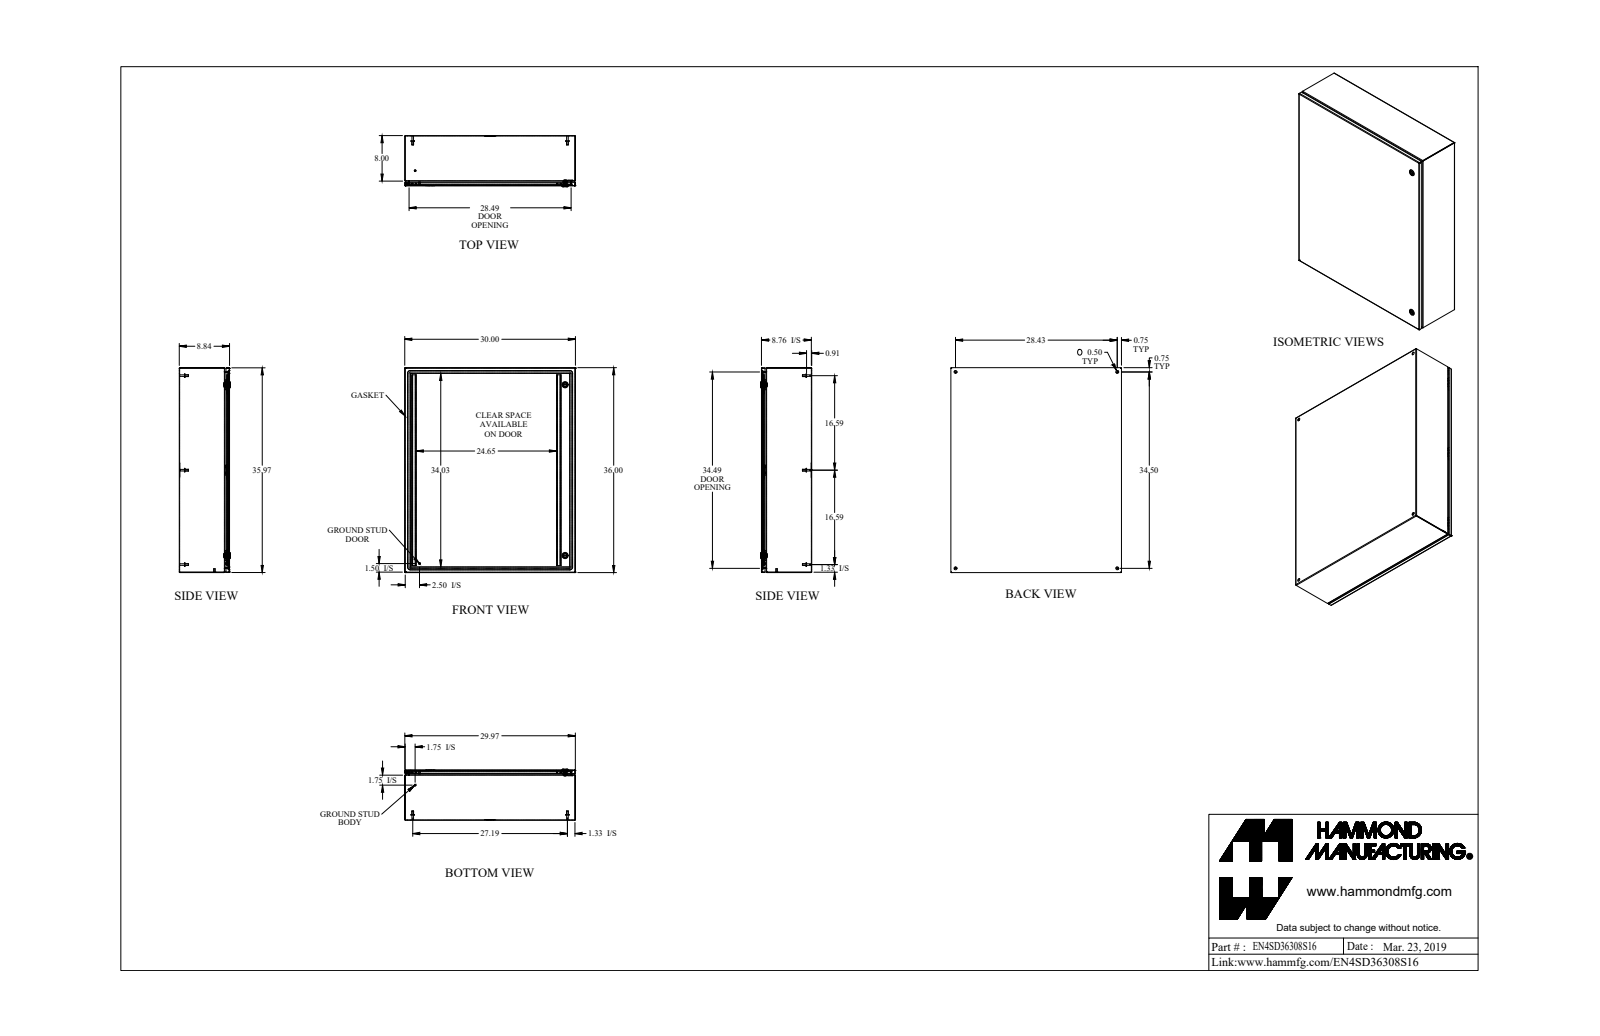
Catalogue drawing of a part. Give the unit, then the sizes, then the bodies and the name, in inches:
Units: inches
Overall size (bounding box): 36 × 30 × 9.002
Round holes (diameter × count): ⌀0.5 ×6, ⌀0.197 ×2, ⌀0.387 ×2, ⌀0.63 ×2, ⌀0.768 ×2, ⌀0.172 ×1, ⌀0.24 ×1, ⌀0.242 ×1
Round bosses / shafts (diameter × count): ⌀0.625 ×8, ⌀0.313 ×8, ⌀0.275 ×6, ⌀1.1 ×2, ⌀0.785 ×2, ⌀0.525 ×2, ⌀0.25 ×2, ⌀0.236 ×2
Partial cylindrical surfaces — rounded edges, fillets, slot ends (radius × count): R0.036 ×20, R0.108 ×20, R0.25 ×16, R0.01 ×12, R0.048 ×12, R0.006 ×6, R0.062 ×6, R0.125 ×4
Main face-to-face distances: 0.072, 8.77, 8.698, 8.842, 29.928, 35.928, 29.856, 30, 35.856, 36
Hole centre spacings: 27.531, 28.428, 34.5, 44.704, 2.457, 2.458, 30, 32.265
Volume: 267.6 in³ · Surface area: 7 508 in²
Bodies: 35 solids, 958 faces (458 planar, 312 cylindrical, 188 other)
Part name (STEP PRODUCT): EN4SD36308S16_Default
STEP written by: SolidWorks 2019 (CONFIG_CONTROL_DESIGN)
